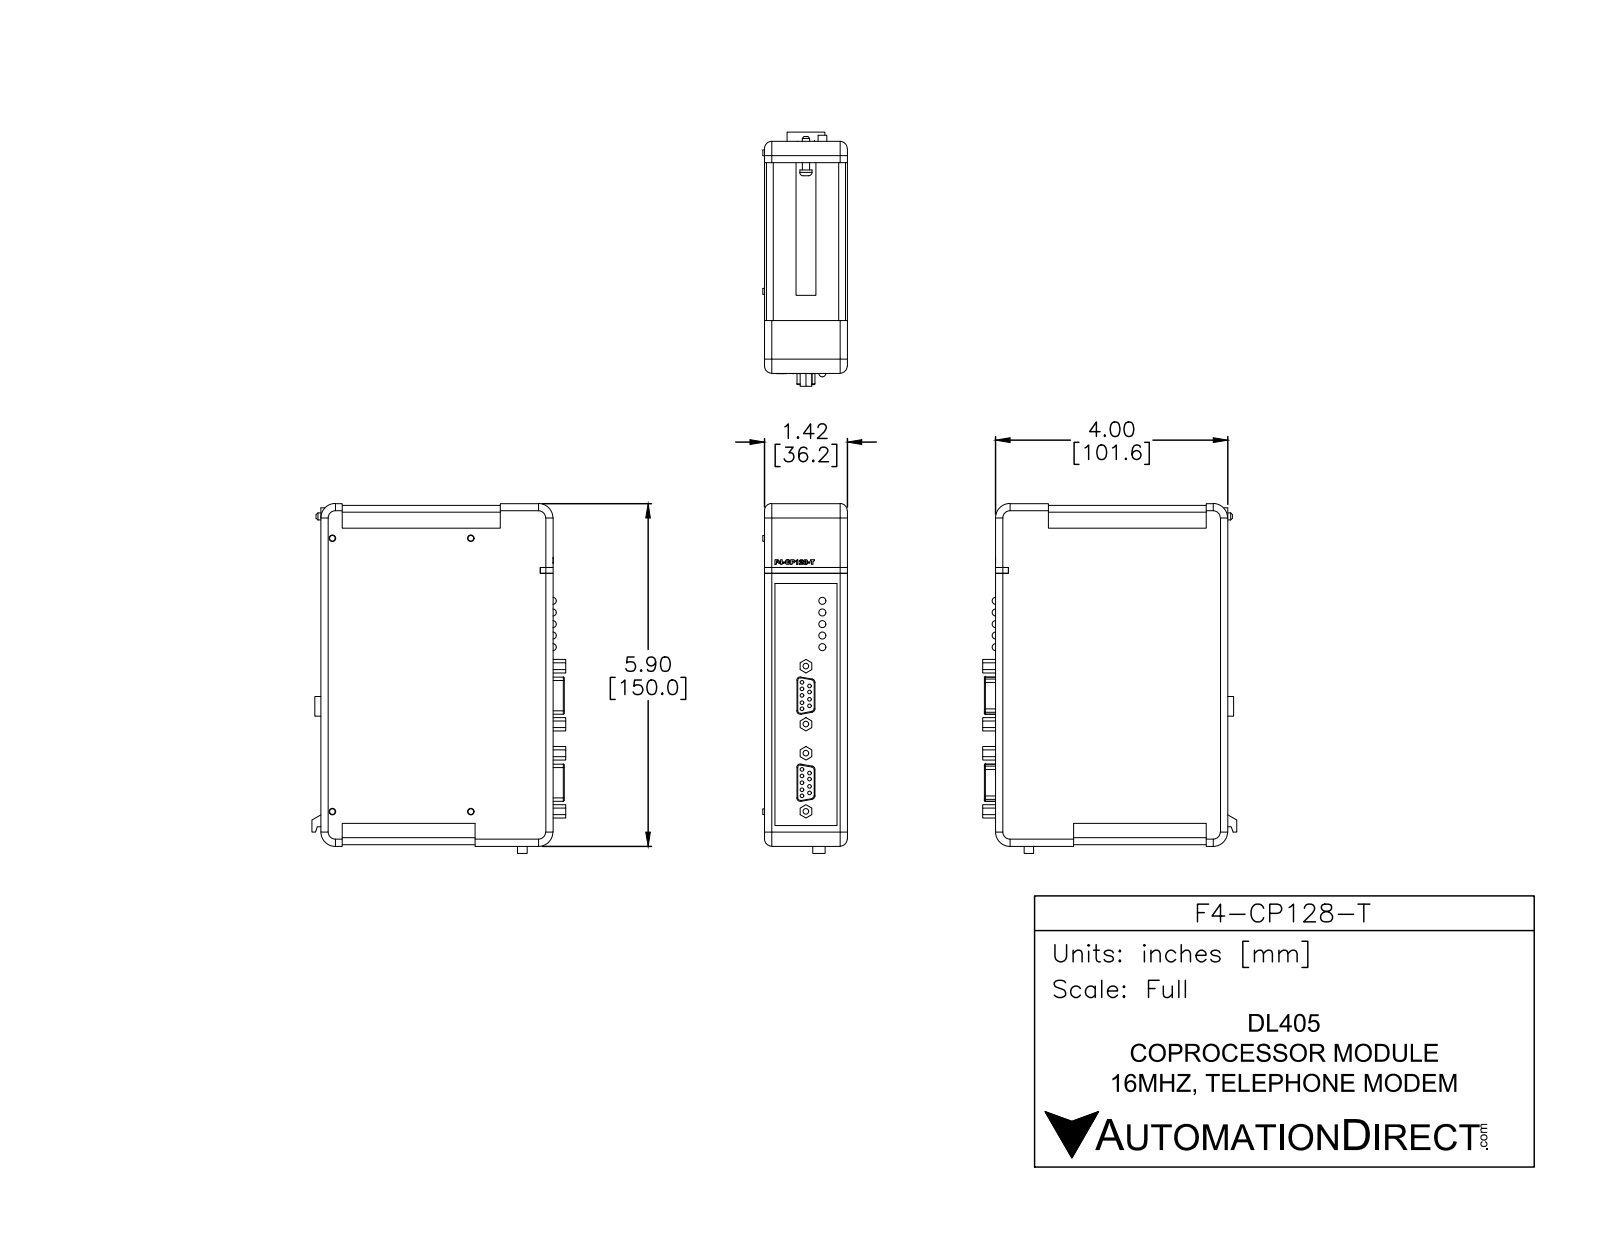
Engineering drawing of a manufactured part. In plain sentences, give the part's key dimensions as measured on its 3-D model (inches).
The part is named "F4-CP128-T". Its 3-D file was written by "SolidWorks 2014 (AUTOMOTIVE_DESIGN)". It is 2 solids with 407 faces: 223 planar, 104 cylindrical and 80 other. Overall it measures 5.905 by 4.375 by 1.455 inches. Its volume is 32.49 cubic inches and its surface area 81.89 square inches. Round holes: 10 of diameter 0.065, 8 of diameter 0.065, 4 of diameter 0.1. Round bosses or shafts: 5 of diameter 0.125, 1 of diameter 0.212, 1 of diameter 0.123. Partial cylindrical surfaces (rounded edges, fillets, slot ends): 8 of radius 0.06, 8 of radius 0.125, 6 of radius 0.015, 4 of radius 0.12, 4 of radius 0.25, 1 of radius 0.145, 1 of radius 0.171. The main face-to-face distances are 1.425, 0.03, 3.97, 1.395, 5.875, 5.845, 4, 0.2, 3.77, 3.8. The hole center spacings are 1.5, 0.113, 0.125, 0.144, 0.146, 0.32, 0.322, 0.103.
